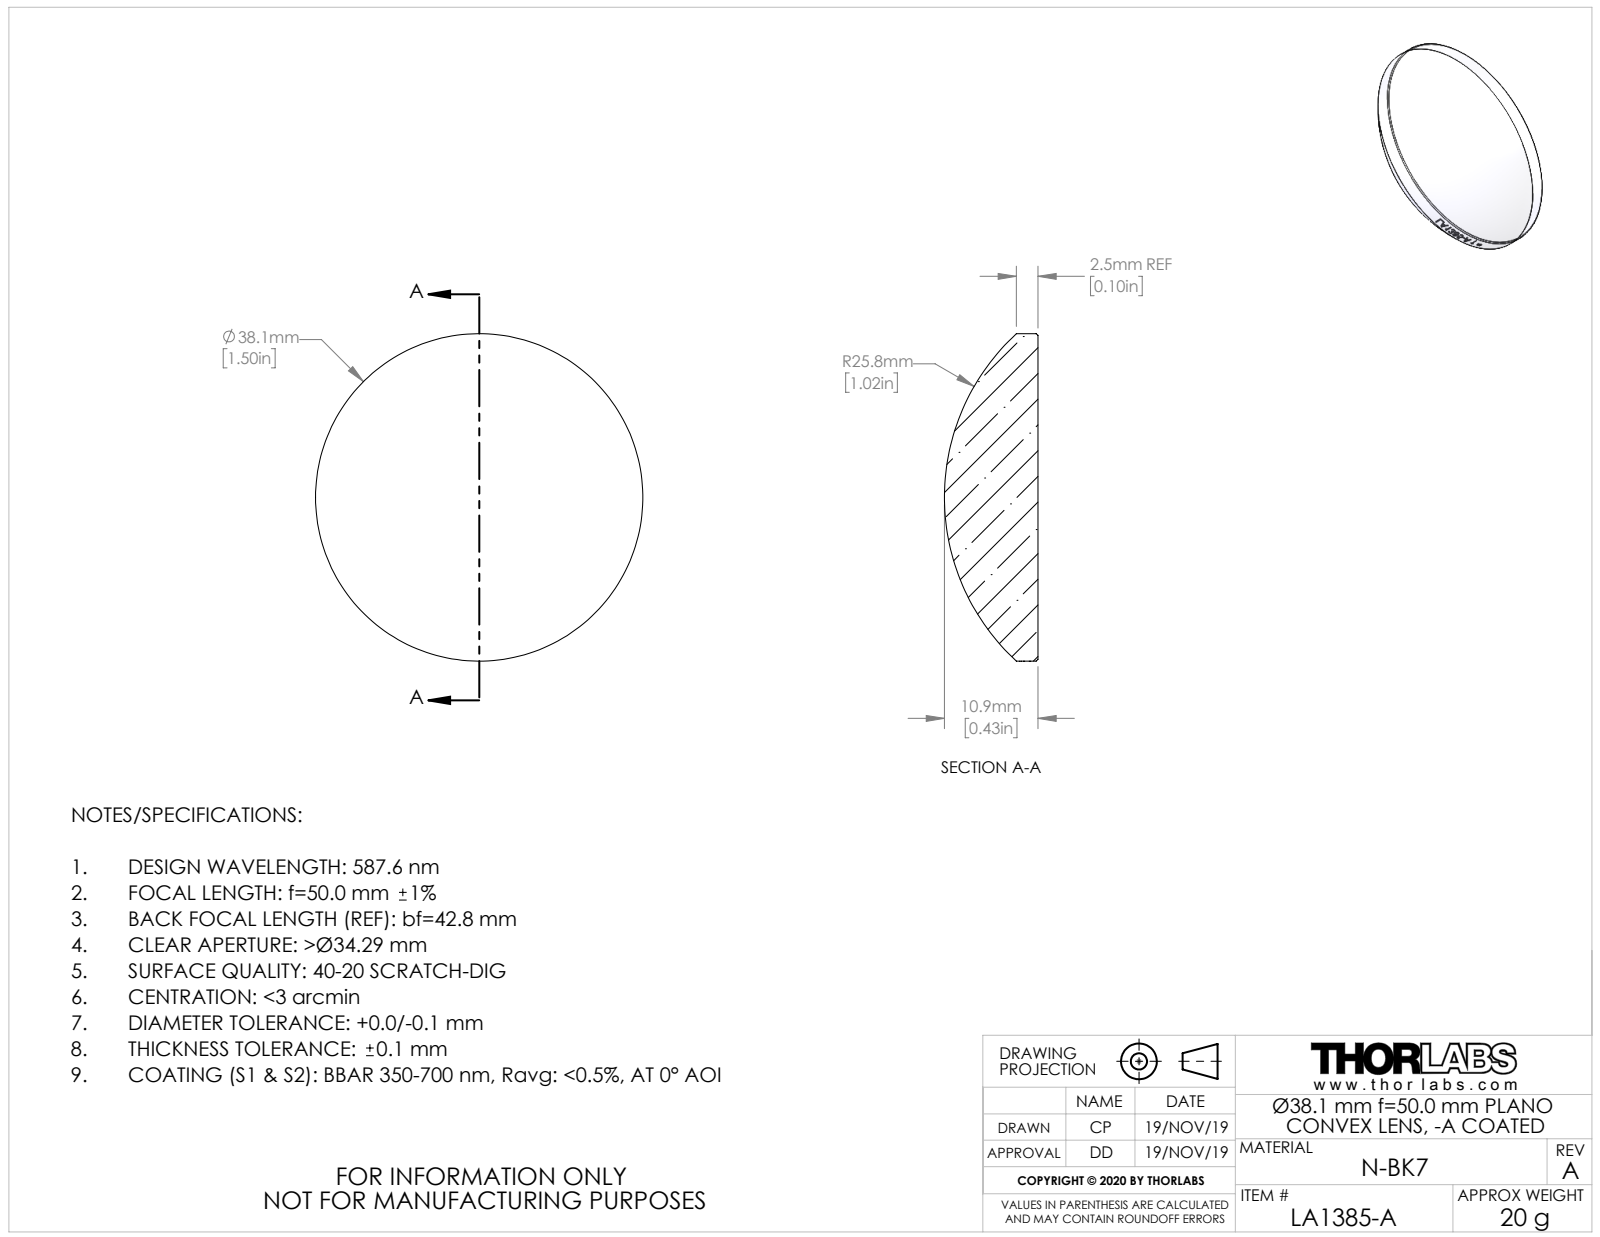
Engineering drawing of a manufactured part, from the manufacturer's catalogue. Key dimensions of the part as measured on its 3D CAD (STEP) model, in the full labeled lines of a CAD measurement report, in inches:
Part name (STEP PRODUCT): TTN200705-E0W
STEP written by: SolidWorks 2018 (CONFIG_CONTROL_DESIGN)
Units: inches
Bodies: 1 solid, 23 faces (1 planar, 18 cylindrical, 4 other)
Overall size (bounding box): 1.5 × 1.5 × 0.428
Volume: 0.484 in³ · Surface area: 4.318 in²
Round bosses / shafts (diameter × count): ⌀1.5 ×1
